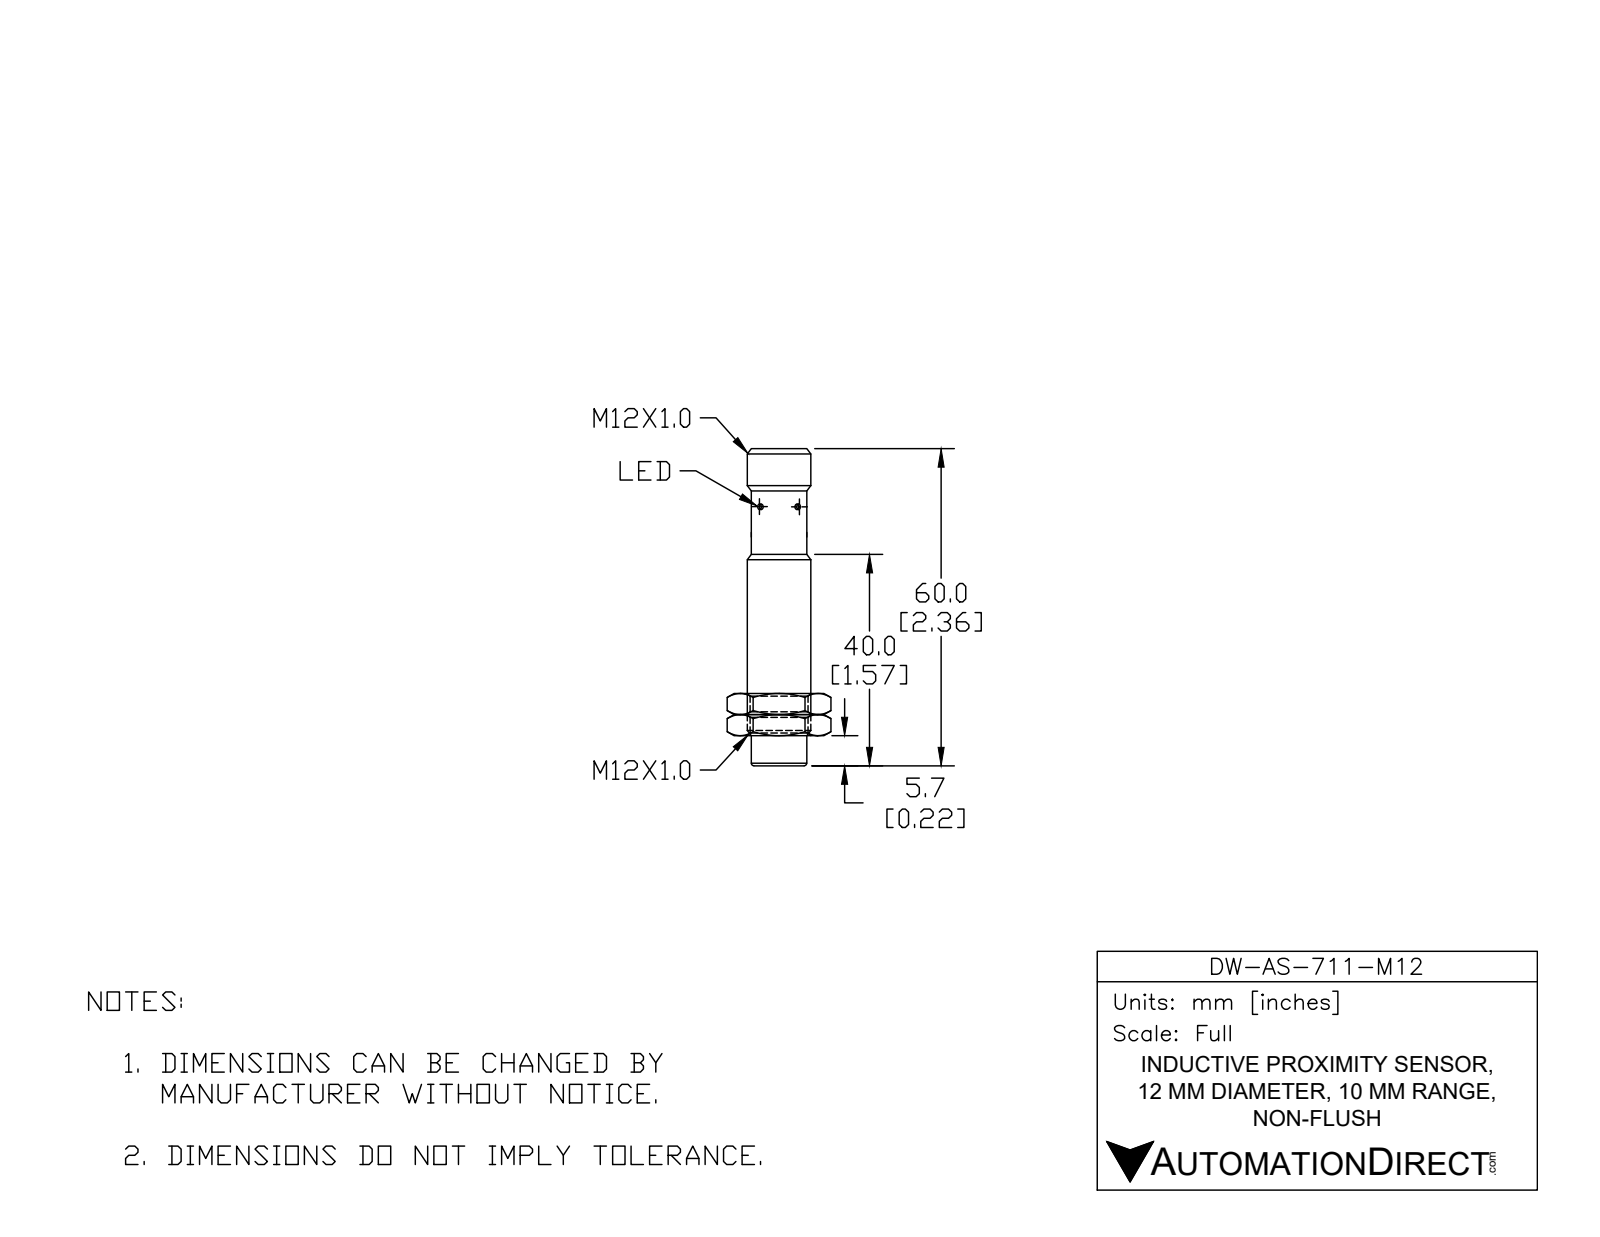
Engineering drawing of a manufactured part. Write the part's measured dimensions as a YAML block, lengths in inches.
part_name: "DW-AS-711-M12"
step_written_by: "SolidWorks 2017 (AUTOMOTIVE_DESIGN)"
units: inches
bodies: {solids: 1, faces: 40, planar: 9, cylindrical: 20, other: 11}
overall_size: [2.362, 0.472, 0.472]
volume: 0.359
surface_area: 4.295
round_holes:
  - {diameter: 0.118, count: 2}
  - {diameter: 0.335, count: 1}
round_bosses_or_shafts:
  - {diameter: 0.04, count: 4}
  - {diameter: 0.472, count: 1}
  - {diameter: 0.415, count: 1}
partial_cylinders:
  - {radius: 0.02, count: 1}
  - {radius: 0.02, count: 1}
  - {radius: 0.193, count: 1}
face_to_face_distances: [2.02, 2.362, 0.343, 1.614, 0.406, 0.748, 2.047, 0.433, 0.028, 0.315]
